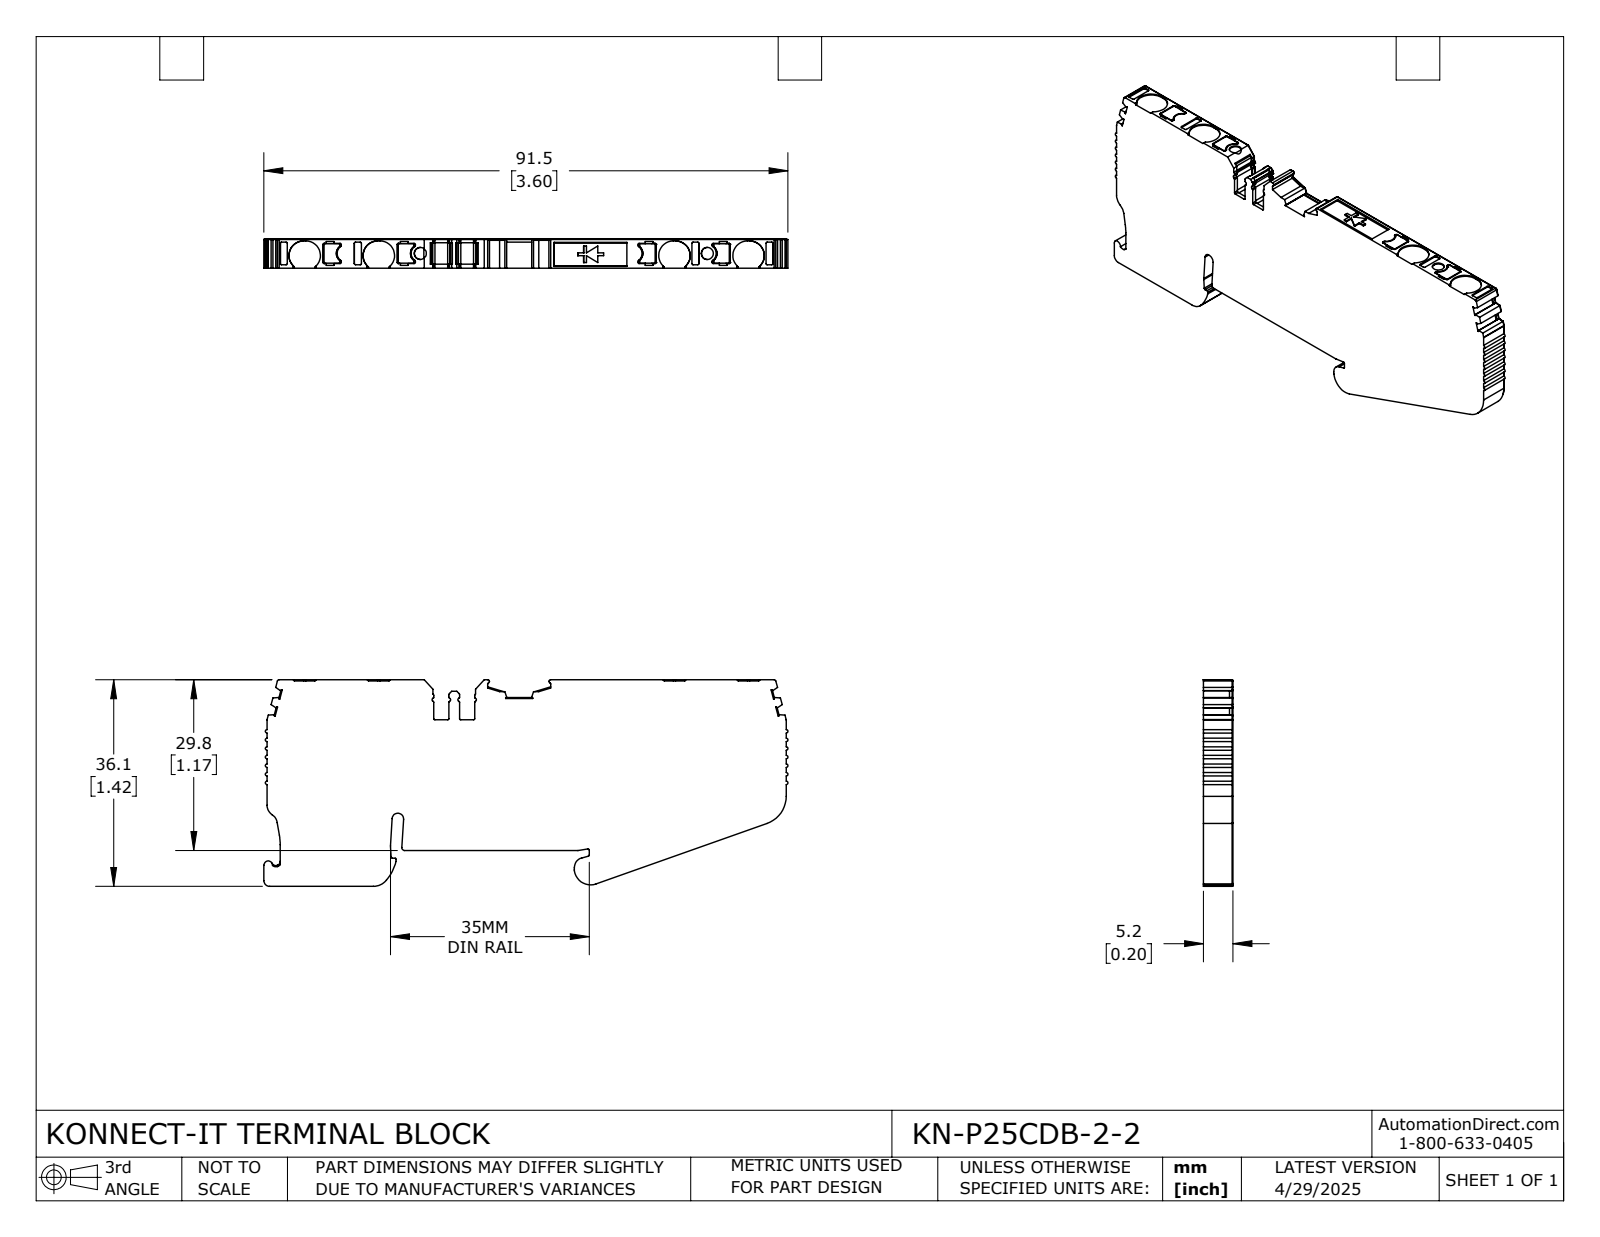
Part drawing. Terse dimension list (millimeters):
name: KN-P25CDB-2-2
written by: SolidWorks 2024 (CONFIG_CONTROL_DESIGN)
unit: mm
bodies: 1 solid, 647 faces (371 planar, 273 cylindrical, 3 other)
size: 91.5 × 36.07 × 5.15
volume: 14 010 mm³; area: 7 146 mm²
holes: 2× ⌀2.1
rounds: 78× R0.2, 39× R0.3, 16× R0.15, 16× R0.5, 13× R0.1, 9× R0.4, 8× R2.55, 4× R1.5
face distances: 5.15, 29.61, 29.81, 6.26, 35.87, 36.07, 90.66, 5, 4.5, 1.2
hole spacings: 50.12
